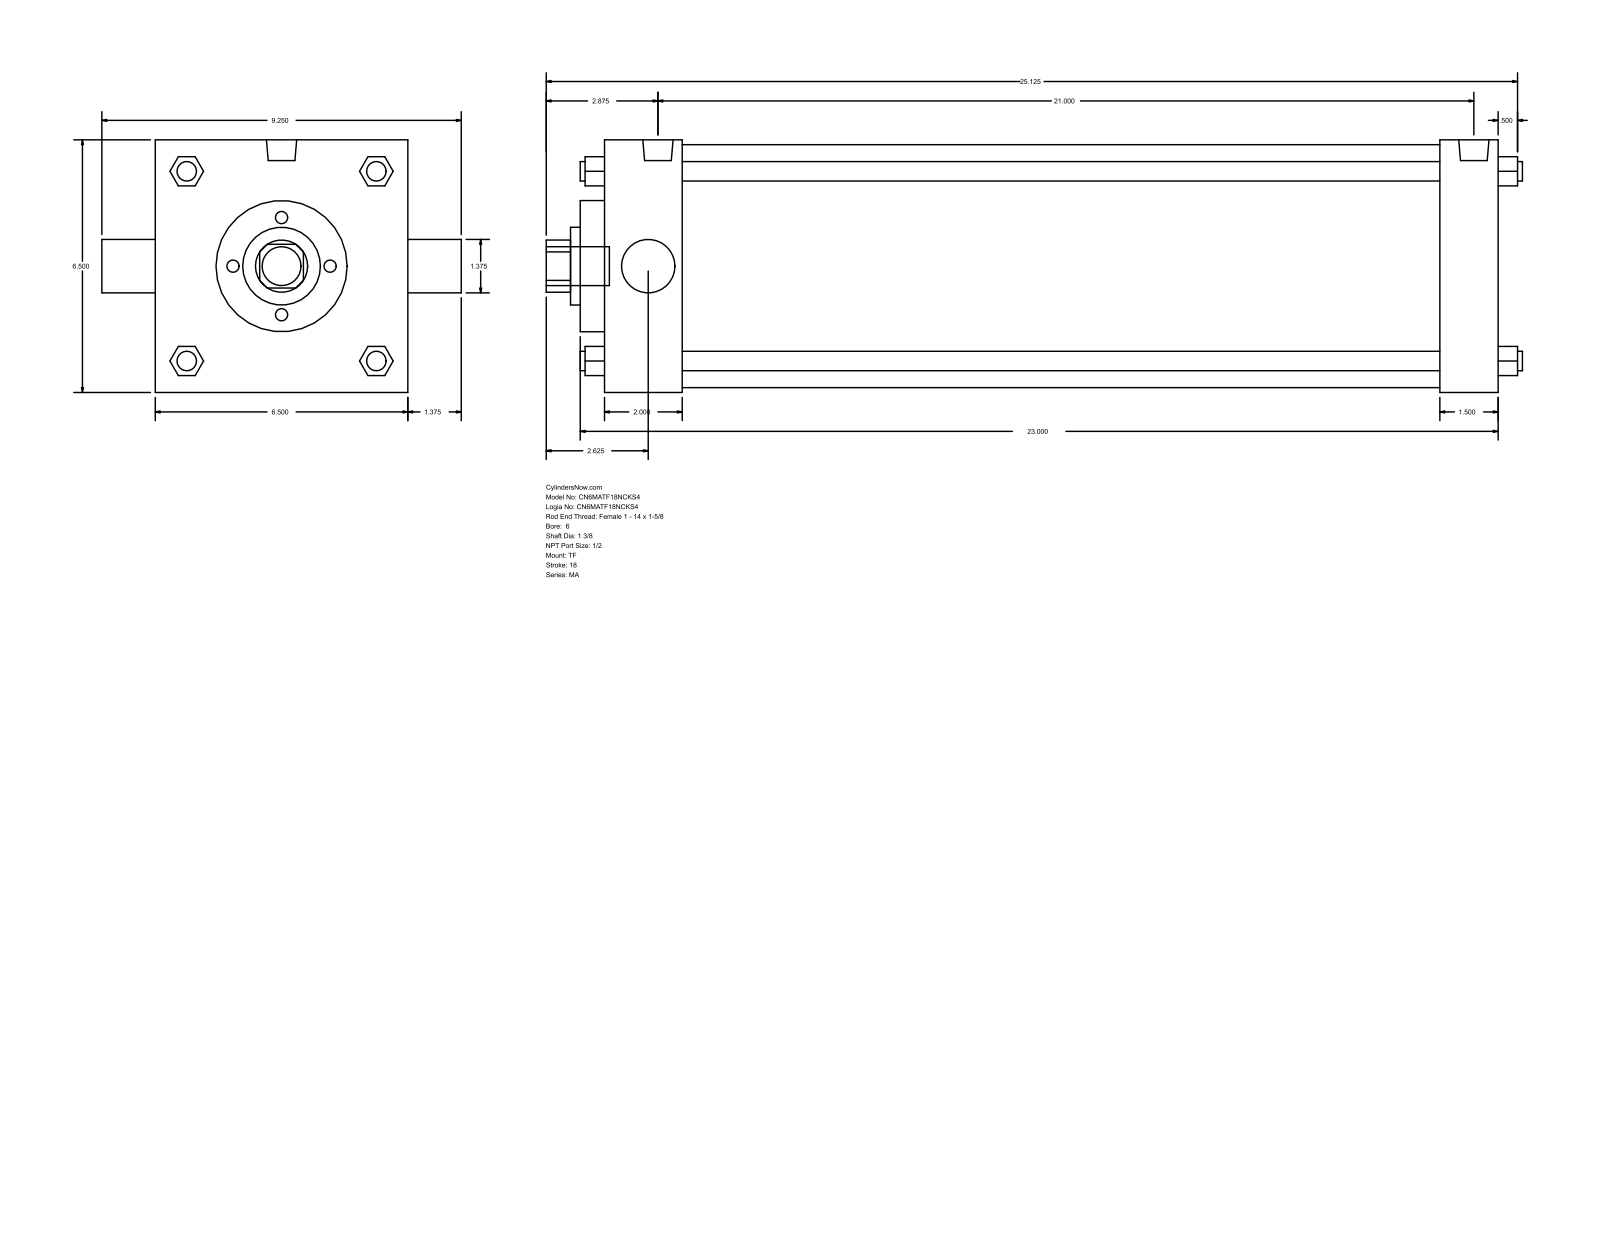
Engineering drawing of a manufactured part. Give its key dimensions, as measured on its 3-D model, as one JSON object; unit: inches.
{"part_name": "MA_TF__0600_1.375", "step_written_by": "GSSL Pune (CONFIG_CONTROL_DESIGN)", "units": "inches", "bodies": {"solids": 0, "faces": 122, "planar": 93, "cylindrical": 29, "other": 0}, "overall_size": [25.125, 9.25, 6.5], "round_holes": [[1.375, 2], [2, 1], [3.375, 1], [6.25, 1]], "round_bosses_or_shafts": [[0.5, 4], [0.687, 3], [0.778, 2], [1, 1]], "partial_cylinders_radius": [[0.672, 1]], "face_to_face_distances": [6.5, 23.125, 1.5, 2, 21.125, 21.625, 19.625, 0.625, 2.625, 22.25]}
